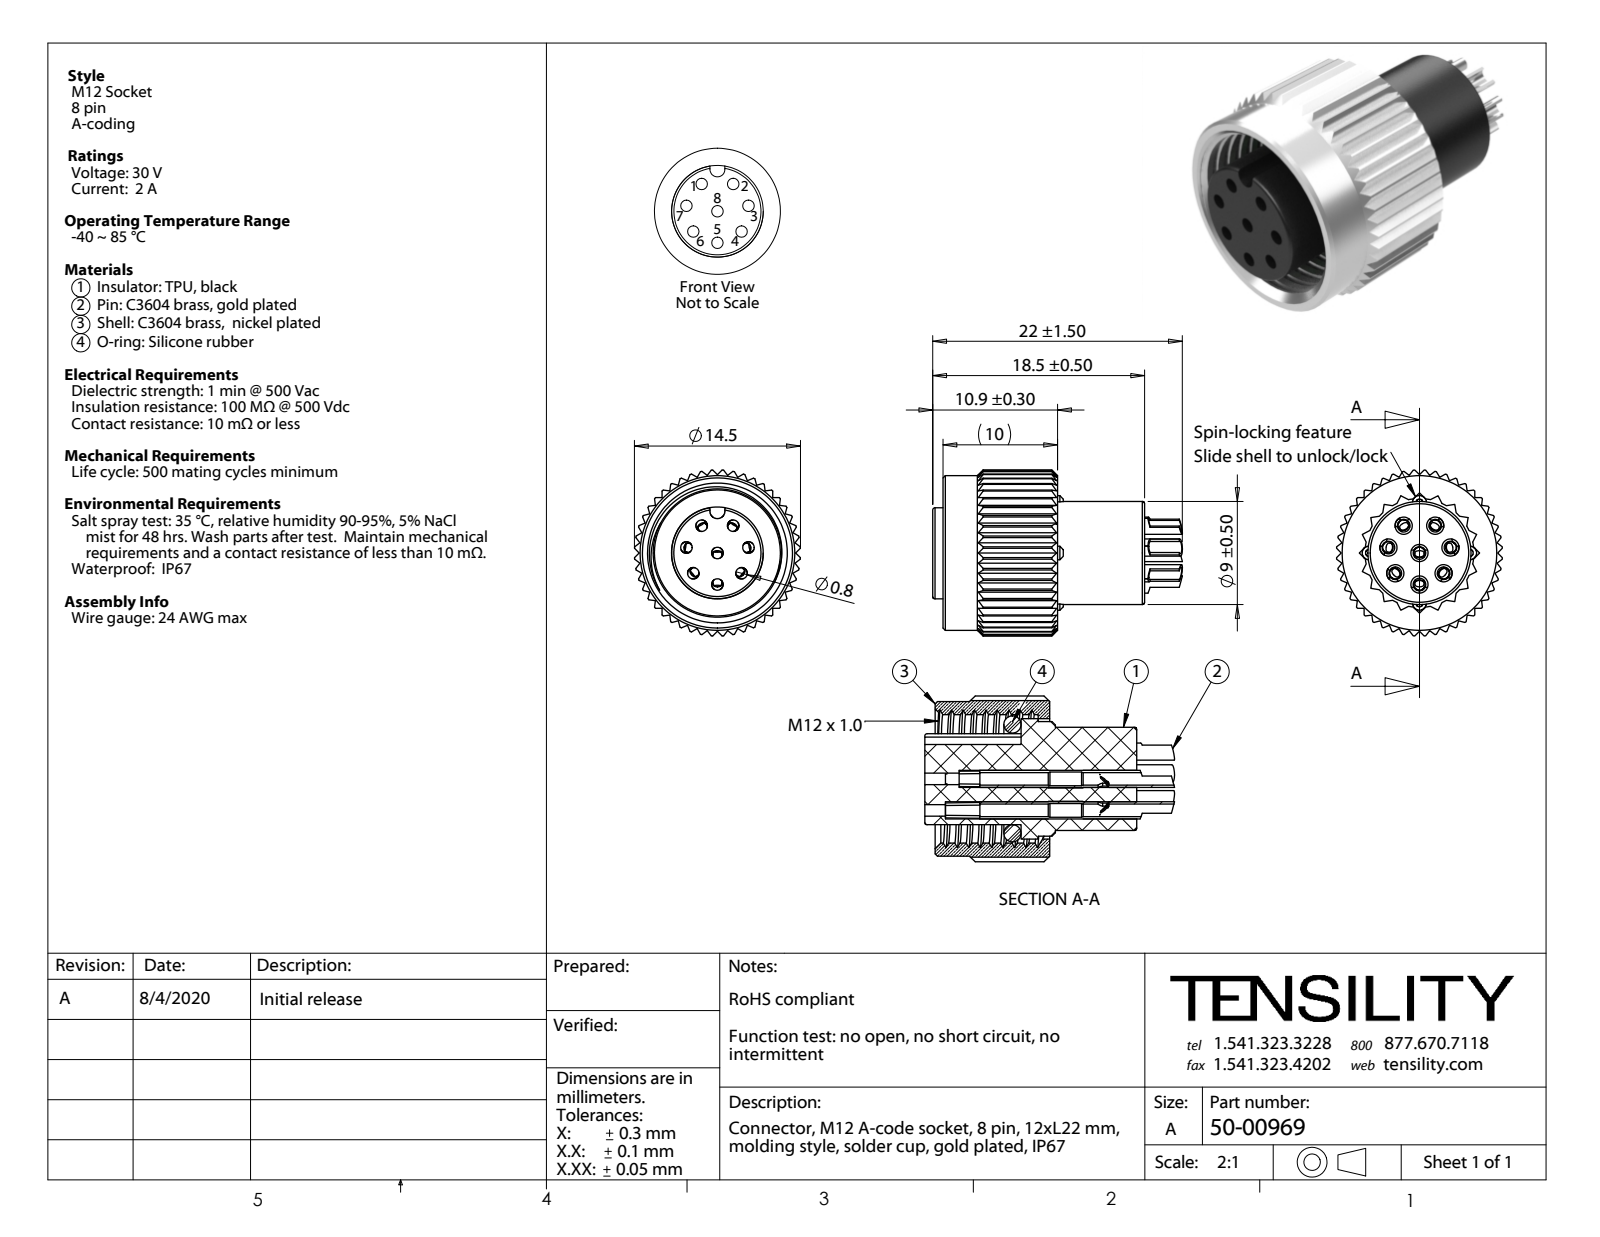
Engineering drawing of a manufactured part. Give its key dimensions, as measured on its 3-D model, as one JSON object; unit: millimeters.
{"part_name": "50-00969; 50-00969-01; 50-00969-03; 50-00969-04 (+1 more)", "step_written_by": "SolidWorks 2015 (CONFIG_CONTROL_DESIGN)", "units": "millimeters", "bodies": {"solids": 11, "faces": 1015, "planar": 374, "cylindrical": 334, "other": 307}, "overall_size": [21.8, 14.48, 14.48], "volume_mm3": 1536, "surface_area_mm2": 3945, "round_holes": [[1, 8], [1.1, 8], [1.2, 8], [11.2, 1]], "round_bosses_or_shafts": [[1.6, 8], [1.5, 8], [13.5, 1], [10.5, 1], [9, 1], [8, 1]], "partial_cylinders_radius": [[0.1, 16], [0.4, 15], [0.6, 4], [0.65, 1], [4.75, 1], [7.25, 1]], "face_to_face_distances": [9.66, 7.6, 10.9, 18.5, 8.4, 2.5, 10.1, 9.9, 1.5, 1], "hole_center_spacings": [2.75, 4.22, 2.33, 5.42, 2.32, 4.5, 5.31, 5.32]}
